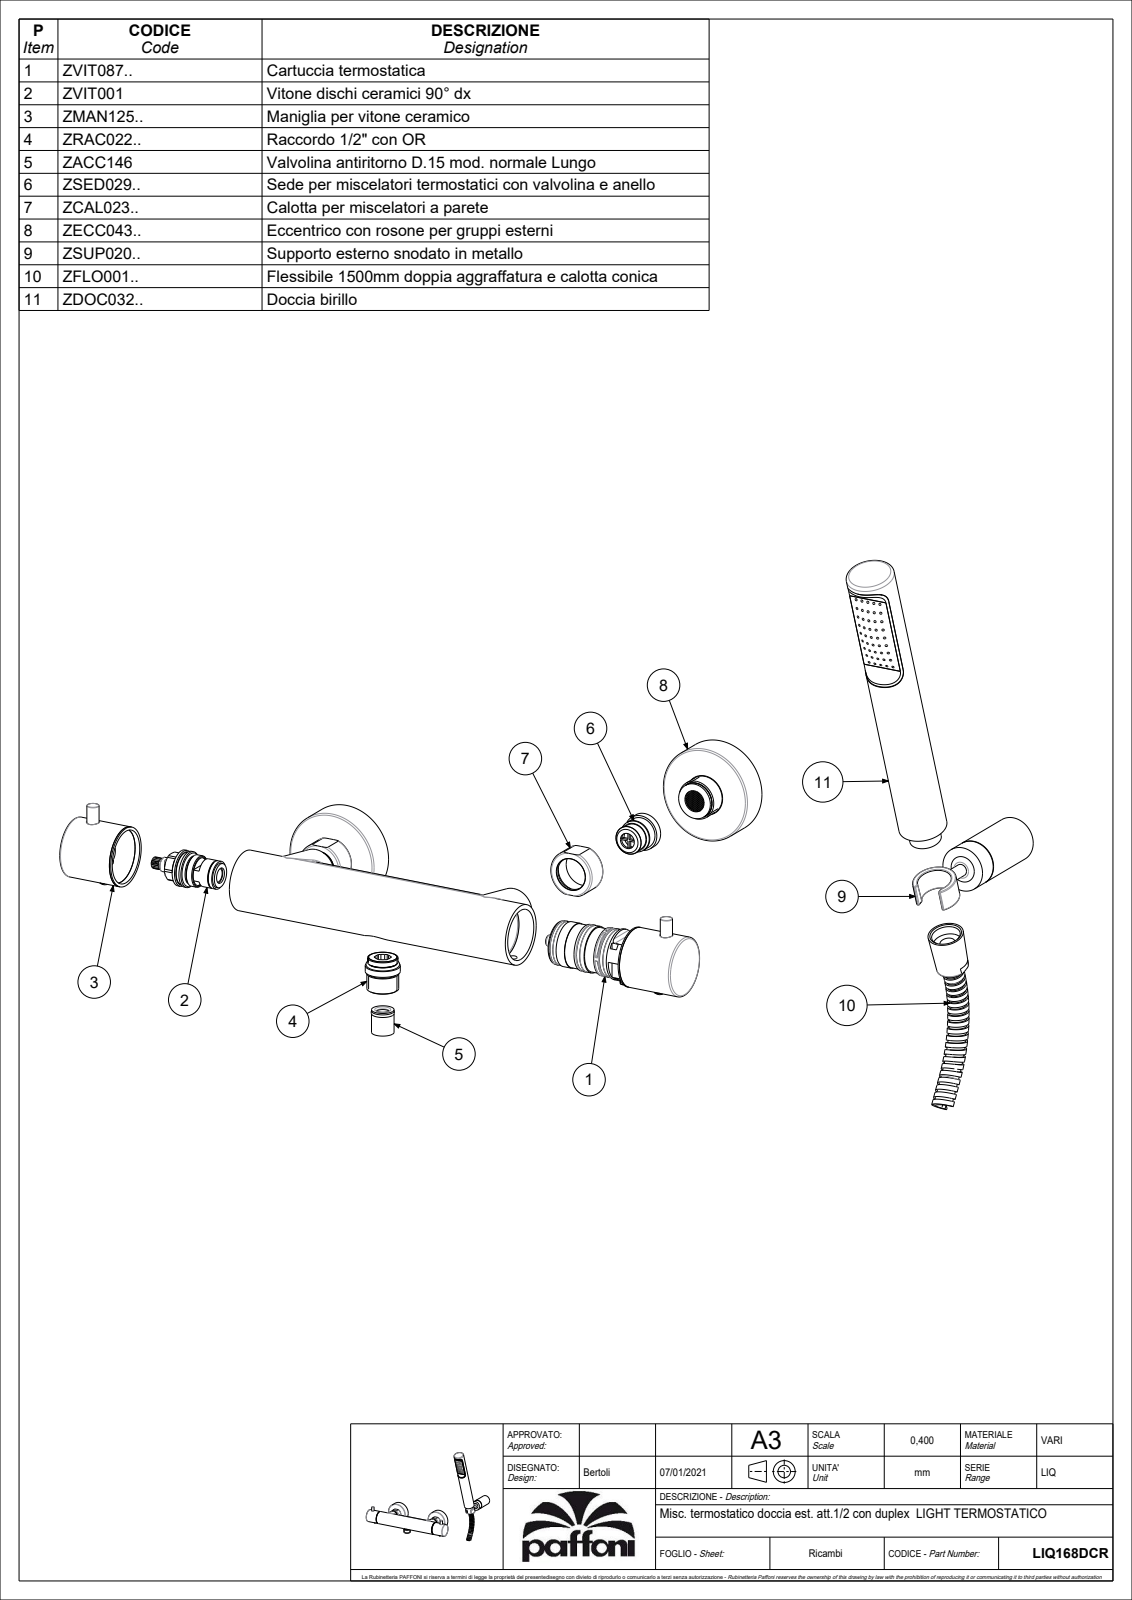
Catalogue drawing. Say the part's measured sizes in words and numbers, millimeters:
The part is named "LIQ168DCR". Its 3-D file was written by "CREO PARAMETRIC BY PTC INC, 2020044 (CONFIG_CONTROL_DESIGN)". It is 4 solids with 738 faces: 287 planar, 218 cylindrical and 233 other. Overall it measures 409.75 by 348.36 by 191.39 millimeters. Its volume is 559 131 cubic millimeters and its surface area 181 234 square millimeters. Round holes: 4 of diameter 4, 3 of diameter 15.1, 2 of diameter 2.5, 2 of diameter 3, 2 of diameter 3.25, 2 of diameter 6, 2 of diameter 10.5, 2 of diameter 16, 2 of diameter 36, 1 of diameter 5.5, 1 of diameter 6.2, 1 of diameter 6.4. Round bosses or shafts: 3 of diameter 8, 2 of diameter 63.5, 2 of diameter 40, 2 of diameter 21.2, 2 of diameter 19, 2 of diameter 7.6, 1 of diameter 40.5, 1 of diameter 32. Partial cylindrical surfaces (rounded edges, fillets, slot ends): 10 of radius 0.5, 4 of radius 1.75, 2 of radius 6.5, 2 of radius 8.5, 2 of radius 15.6, 2 of radius 19.92, 1 of radius 2.75, 1 of radius 5.15. The main face-to-face distances are 3, 20, 42.5, 45.25, 62.5, 65.25, 2.75, 208.96, 4, 209. The hole center spacings are 5, 9, 14.95, 15.2, 98.1, 120.5, 129.5, 150.
